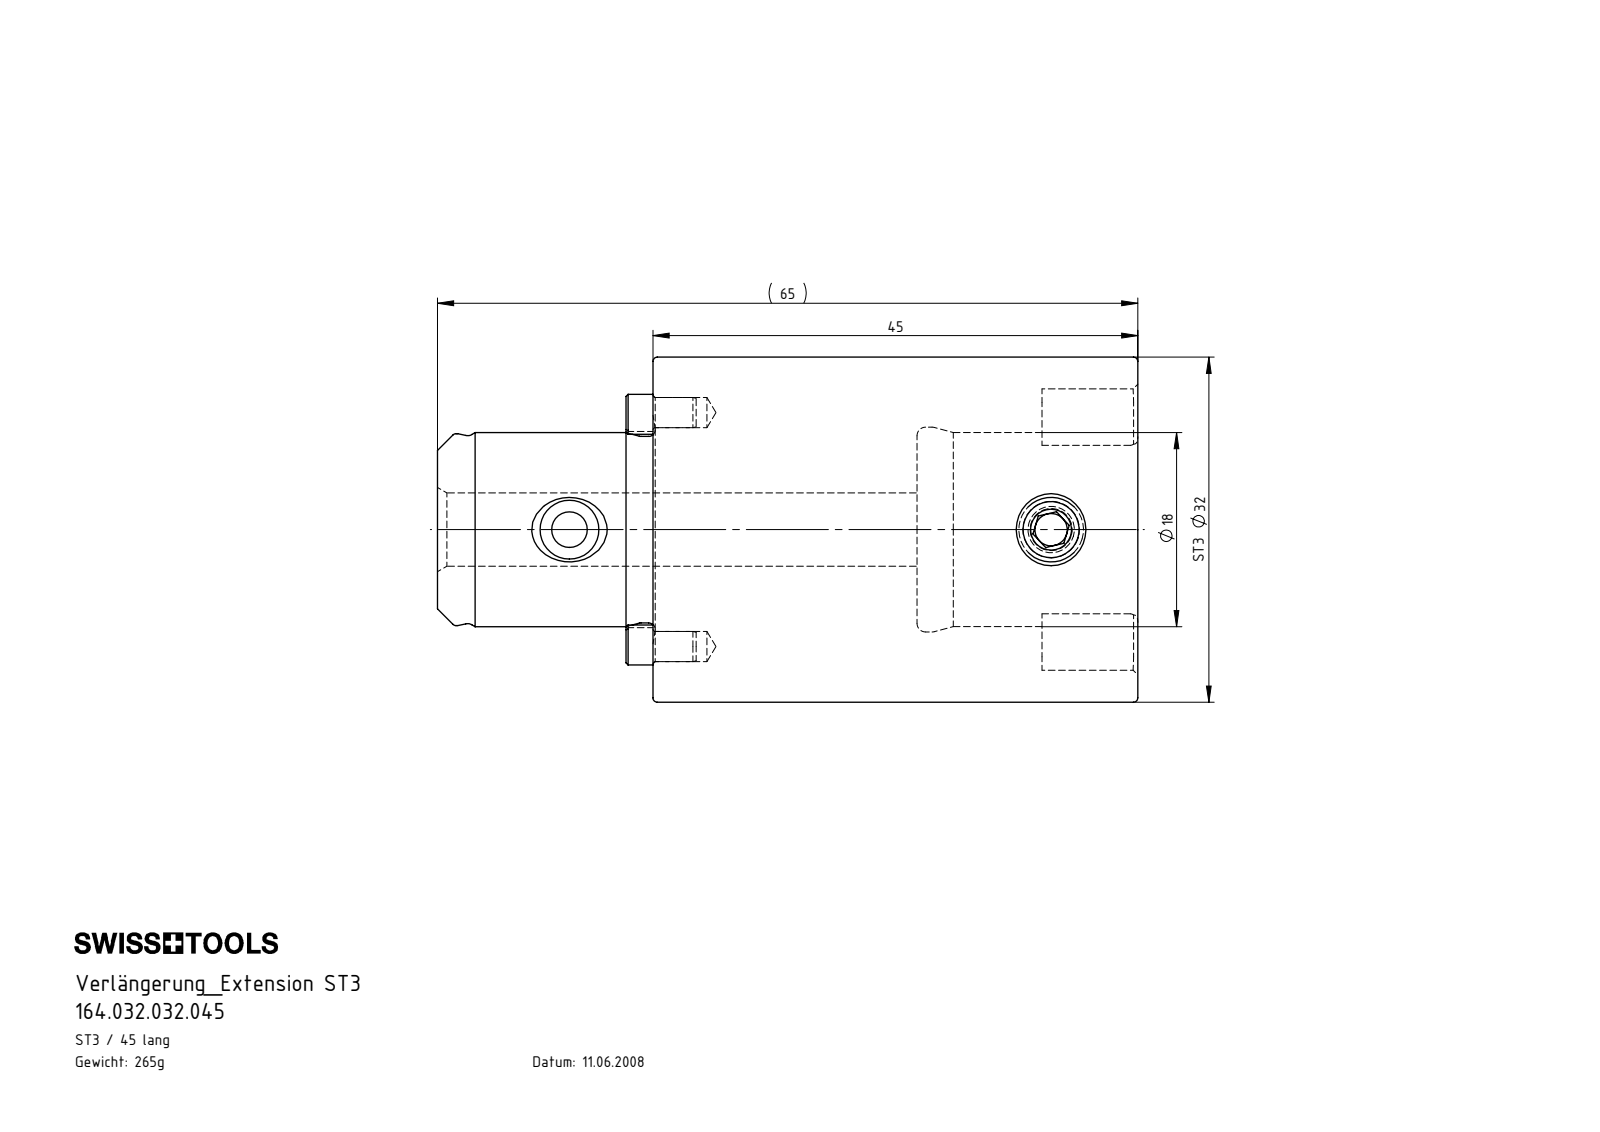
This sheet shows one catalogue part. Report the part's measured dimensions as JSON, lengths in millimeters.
{"part_name": "ST3-ST3.K01.045; ST3-ST3.K01.045_A; ST3-ER1.001.008_A; ST3-ER2.001.007_A", "step_written_by": "SolidWorks 2015 (CONFIG_CONTROL_DESIGN)", "units": "millimeters", "bodies": {"solids": 4, "faces": 150, "planar": 26, "cylindrical": 43, "other": 81}, "overall_size": [65, 32, 32], "volume_mm3": 33820, "surface_area_mm2": 9934, "round_holes": [[2.8, 2], [3.3, 1], [5.25, 1], [6.8, 1], [18, 1], [19, 1]], "round_bosses_or_shafts": [[32, 1], [17.8, 1], [17.3, 1], [6, 1]], "partial_cylinders_radius": [[0.5, 4], [2.5, 2], [2.73, 2], [9.05, 2]], "face_to_face_distances": [45, 20.5, 24.5, 20, 44.5, 65, 15.54, 56.1, 36.1, 11.6], "hole_center_spacings": [10.85, 21.7, 44.7]}
